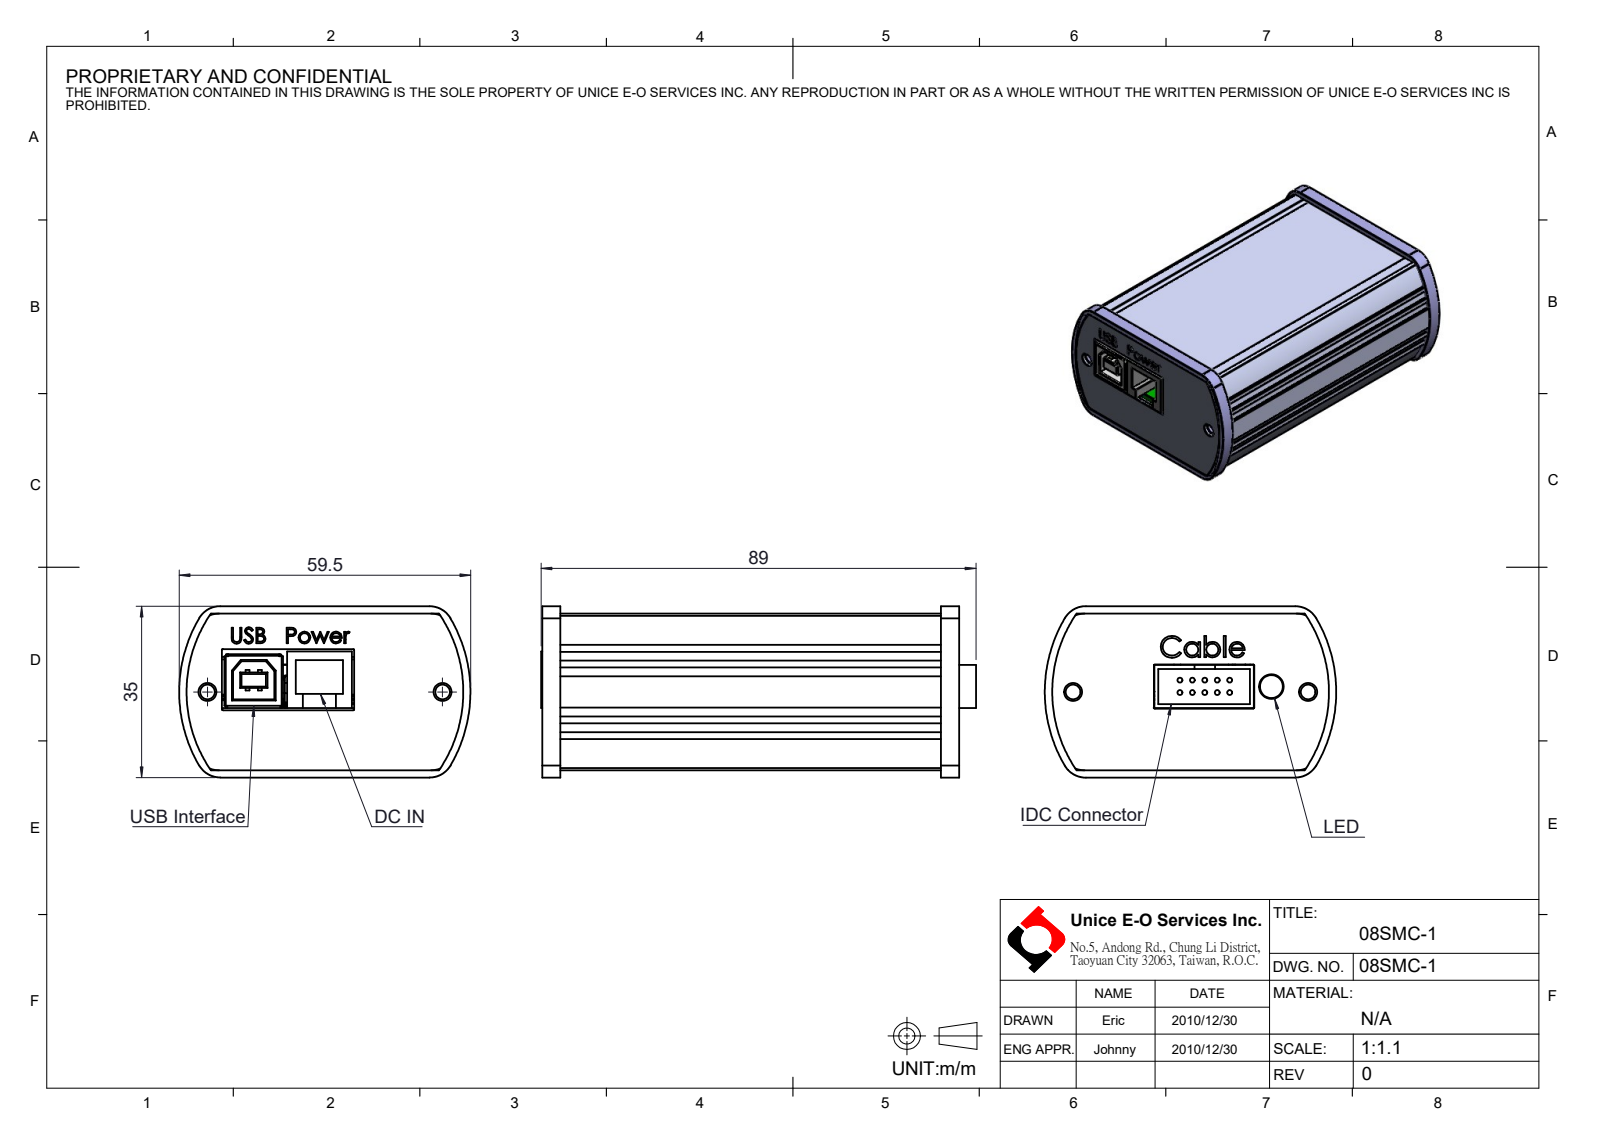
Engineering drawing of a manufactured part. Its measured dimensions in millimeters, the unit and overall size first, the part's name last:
Units: millimetres
Overall size (bounding box): 88.78 × 59.5 × 35
Round holes (diameter × count): ⌀1.2 ×6, ⌀3 ×4, ⌀8.2 ×3, ⌀0.83 ×2, ⌀3.7 ×2, ⌀0.89 ×1, ⌀5 ×1
Round bosses / shafts (diameter × count): ⌀1 ×35, ⌀8 ×3, ⌀7 ×3, ⌀0.55 ×3, ⌀0.52 ×2, ⌀4.7 ×1, ⌀3.35 ×1, ⌀3.3 ×1
Partial cylindrical surfaces — rounded edges, fillets, slot ends (radius × count): R1 ×20, R0.3 ×13, R0.13 ×12, R0.2 ×8, R0.25 ×8, R5 ×8, R0.65 ×6, R3 ×5
Main face-to-face distances: 1.4, 28.6, 1, 8.6, 1.7, 20, 18.6, 10, 2.4, 10.3
Hole centre spacings: 1.35, 14.48, 2.7, 30.64, 39.38, 14.42, 14.67, 29.51
Volume: 43 357 mm³ · Surface area: 58 784 mm²
Bodies: 90 solids, 3371 faces (2445 planar, 585 cylindrical, 341 other)
Part name (STEP PRODUCT): 08SMC-1
STEP written by: SolidWorks 2016 (CONFIG_CONTROL_DESIGN)
